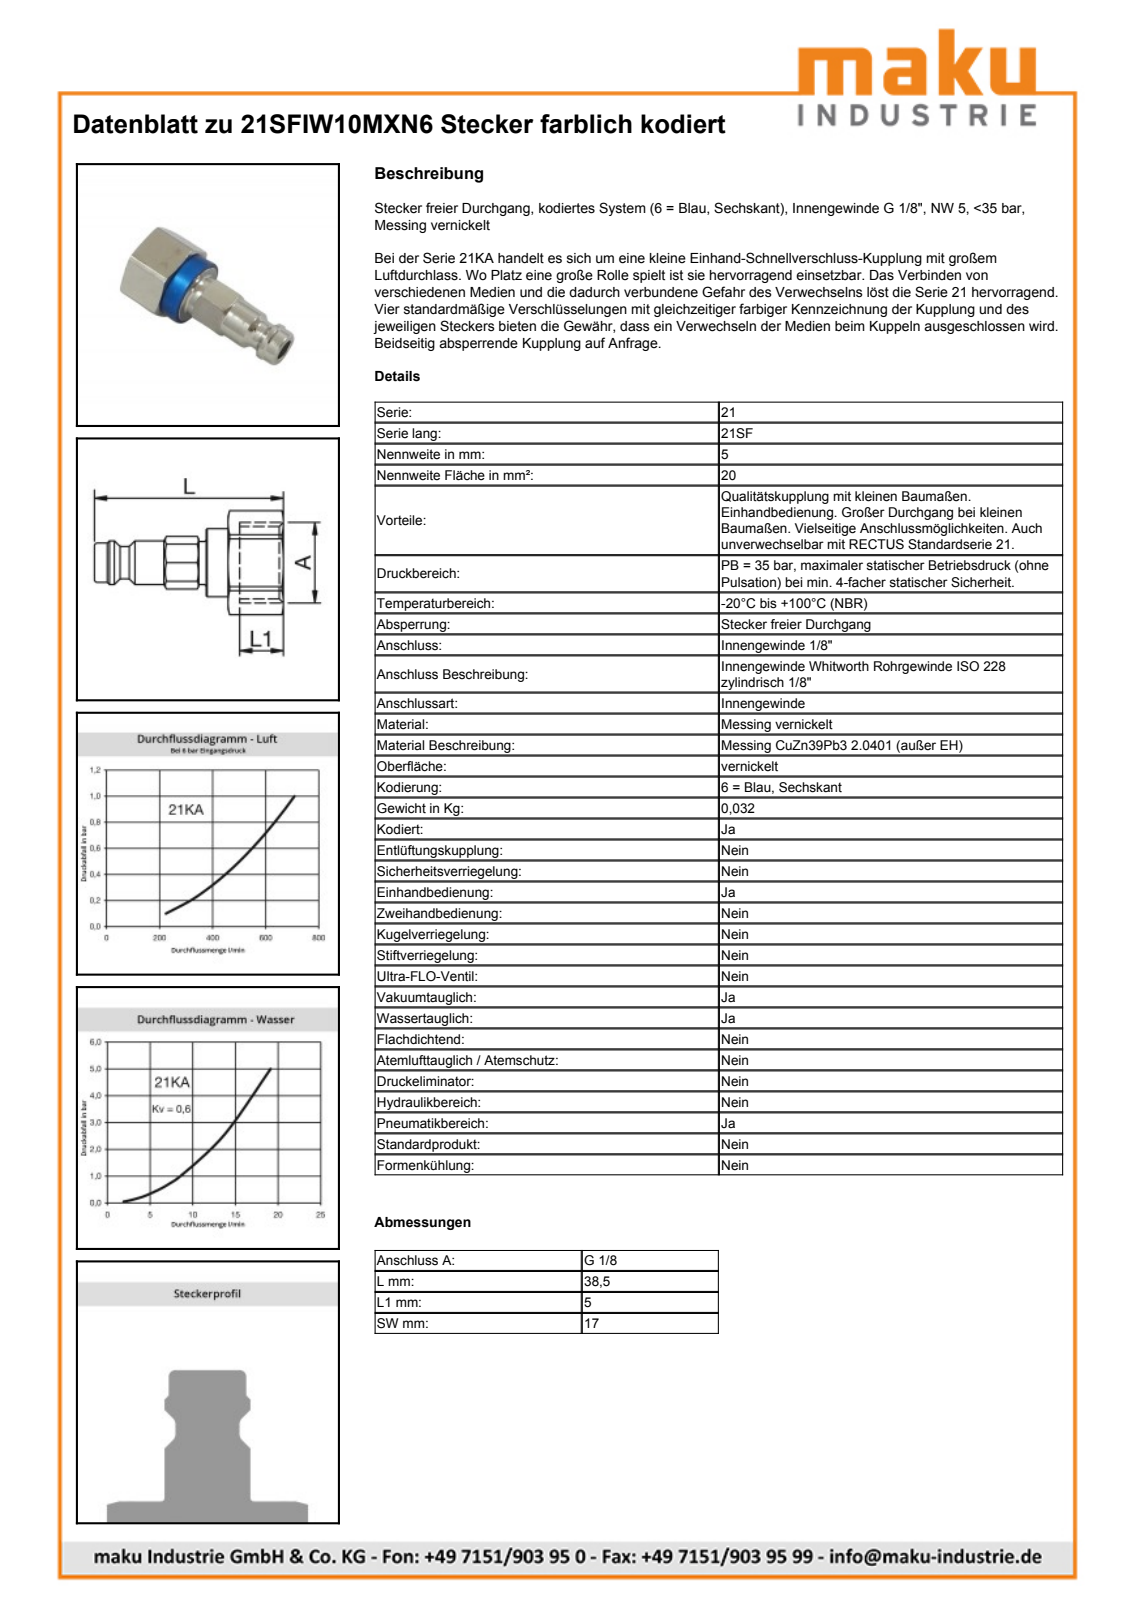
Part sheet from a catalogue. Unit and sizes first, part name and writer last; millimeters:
Units: millimetres
Overall size (bounding box): 39.5 × 15.8 × 15.5
Round holes (diameter × count): ⌀4.95 ×1, ⌀9.73 ×1, ⌀13.85 ×1, ⌀14.05 ×1
Round bosses / shafts (diameter × count): ⌀15.5 ×1, ⌀14 ×1, ⌀9.7 ×1, ⌀9 ×1, ⌀8.1 ×1, ⌀6.65 ×1
Partial cylindrical surfaces — rounded edges, fillets, slot ends (radius × count): R5.7 ×1, R7.9 ×1
Main face-to-face distances: 14, 2, 12, 10, 8, 16, 4.2, 3.8, 11.8, 23.5
Volume: 3 131 mm³ · Surface area: 2 900 mm²
Bodies: 2 solids, 68 faces (18 planar, 23 cylindrical, 27 other)
Part name (STEP PRODUCT): D113143; D113144; D113145
STEP written by: Autodesk Inventor 2013 (AUTOMOTIVE_DESIGN)
